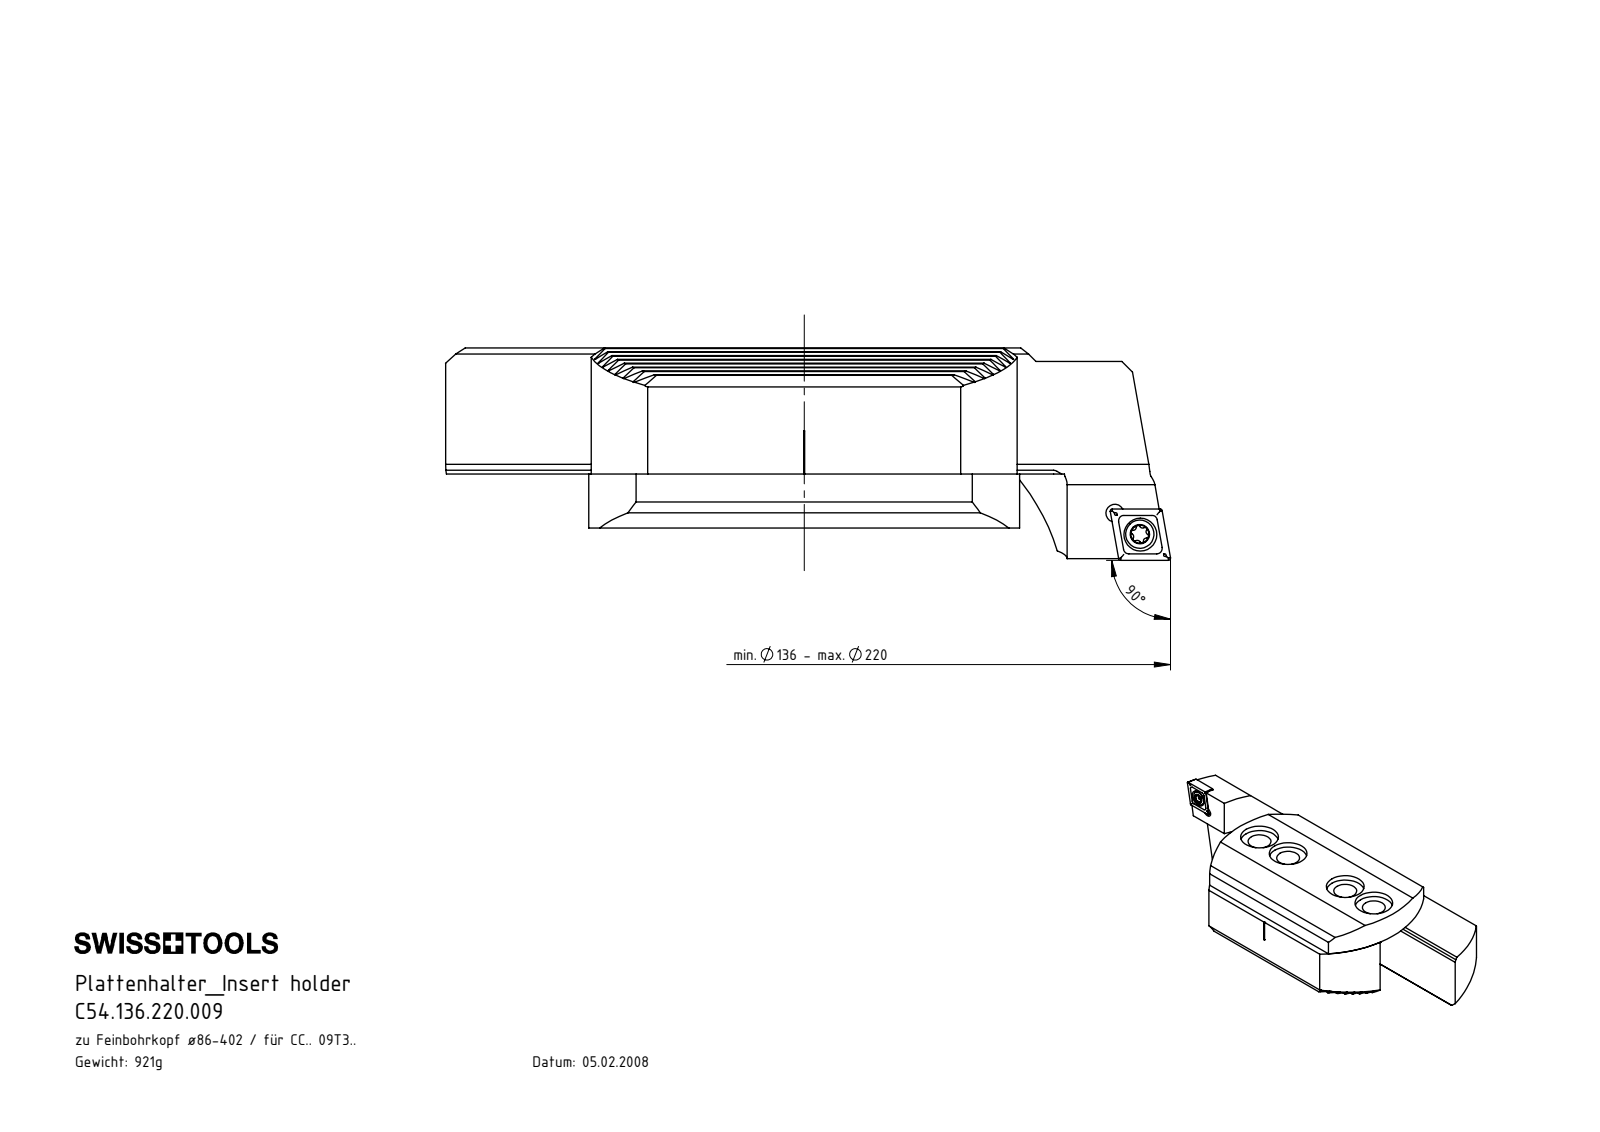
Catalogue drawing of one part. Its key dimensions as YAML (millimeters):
part_name: "C54.136.220.009; F00-WCB.136.003_B; F00-WCB.136.002_A; F00-WCB.136.001 (+3 more)"
step_written_by: "SolidWorks 2017 (CONFIG_CONTROL_DESIGN)"
units: millimeters
bodies: {solids: 5, faces: 639, planar: 386, cylindrical: 67, other: 186}
overall_size: [134.57, 55, 39.4]
volume: 117330
surface_area: 31785
round_holes:
  - {diameter: 8.5, count: 4}
  - {diameter: 14, count: 4}
  - {diameter: 3.3, count: 2}
  - {diameter: 4.4, count: 1}
  - {diameter: 6.1, count: 1}
round_bosses_or_shafts:
  - {diameter: 5.25, count: 1}
  - {diameter: 4, count: 1}
partial_cylinders:
  - {radius: 0.2, count: 16}
  - {radius: 0.34, count: 6}
  - {radius: 0.59, count: 6}
  - {radius: 40, count: 6}
  - {radius: 0.8, count: 1}
face_to_face_distances: [2.38, 4.76, 21.3, 33.7, 7.14, 12.4, 9.52, 10, 9.53, 7.15]
hole_center_spacings: [15, 45, 6.06, 6.19, 30, 60]
